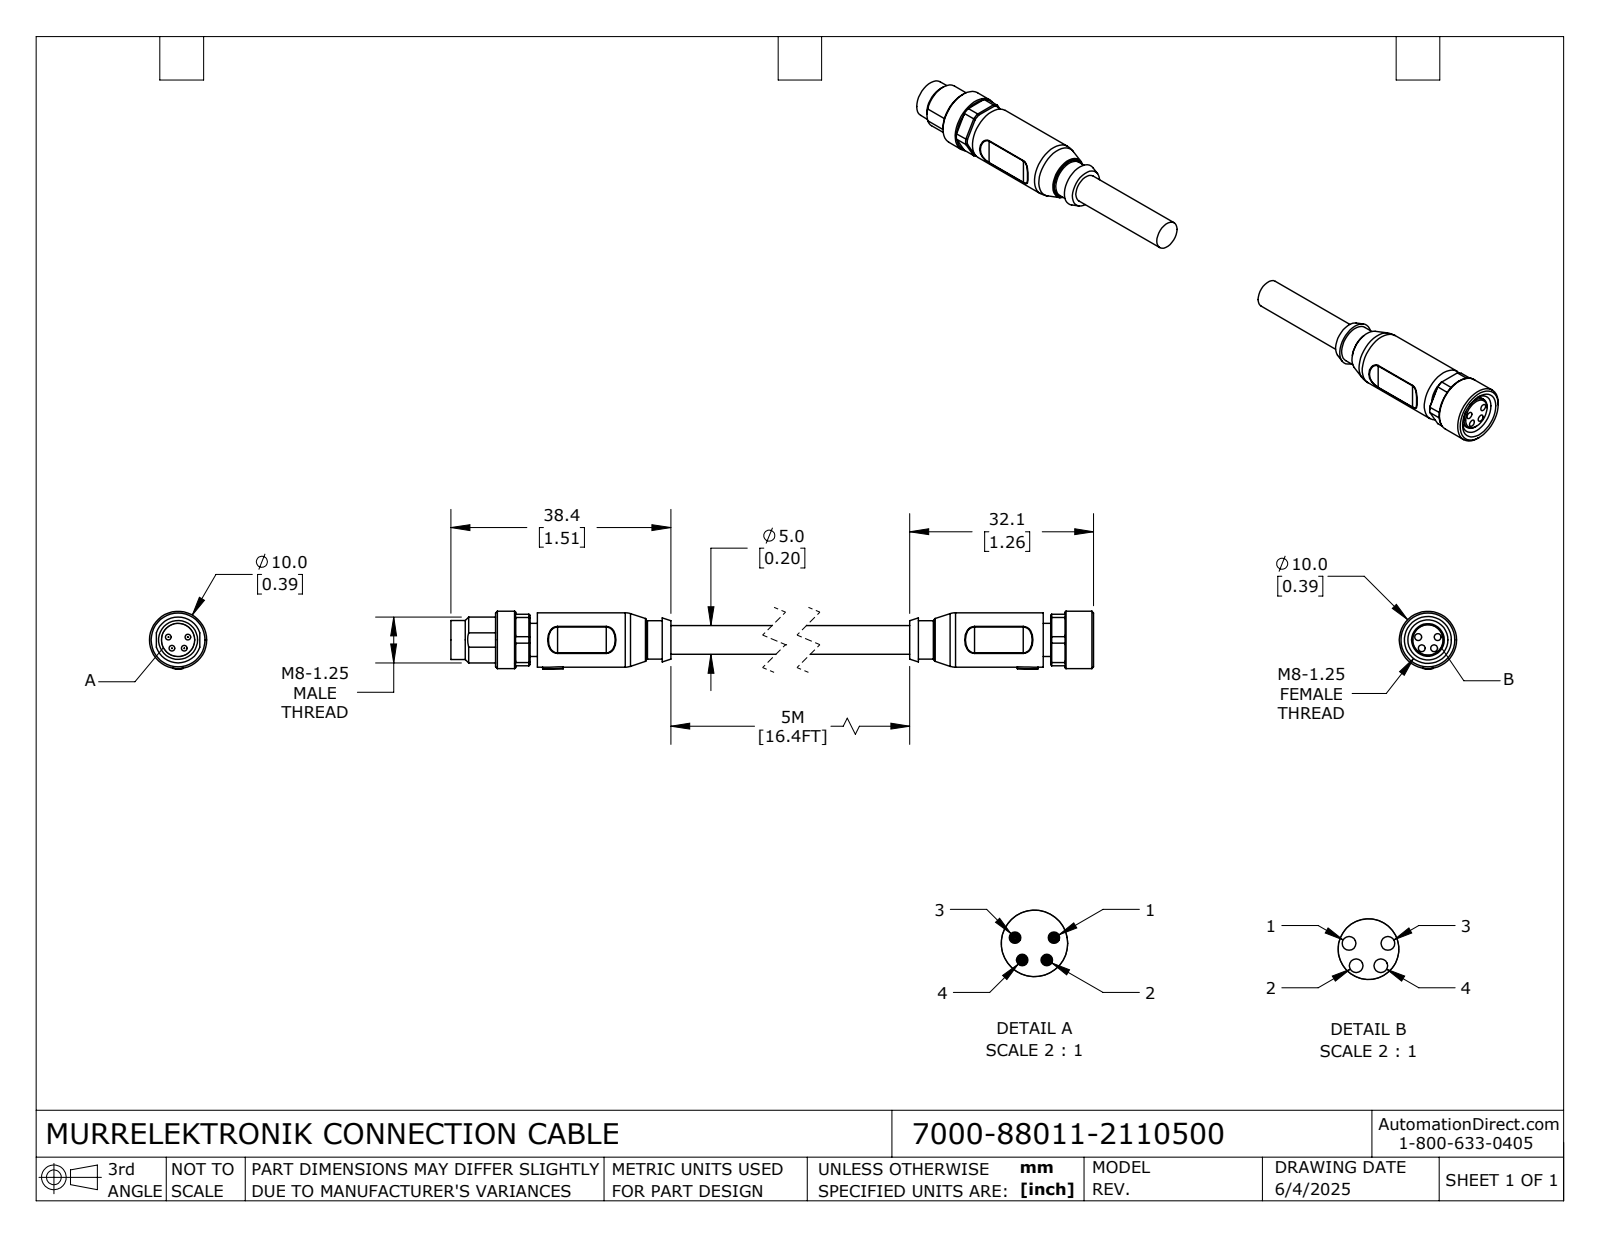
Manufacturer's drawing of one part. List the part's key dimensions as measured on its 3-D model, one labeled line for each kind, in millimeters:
Part name (STEP PRODUCT): 7000-88011-2110500; 7000-88011-2110500_FEMALE; 7000-88011-2110500_MALE
STEP written by: SolidWorks 2024 (CONFIG_CONTROL_DESIGN)
Units: millimetres
Bodies: 2 solids, 226 faces (70 planar, 88 cylindrical, 68 other)
Overall size (bounding box): 135.5 × 10.05 × 10
Volume: 4 815 mm³ · Surface area: 3 452 mm²
Round holes (diameter × count): ⌀1.2 ×4, ⌀7 ×1
Round bosses / shafts (diameter × count): ⌀1 ×4, ⌀10 ×1, ⌀9.5 ×1, ⌀8 ×1, ⌀6.8 ×1, ⌀6.7 ×1, ⌀5.8 ×1, ⌀5.7 ×1
Partial cylindrical surfaces — rounded edges, fillets, slot ends (radius × count): R2.5 ×8, R0.2 ×4, R4.9 ×1, R5.05 ×1
Main face-to-face distances: 8.3, 1.3, 112.9, 9, 121.7, 111.6, 24.6, 8.8, 44.6, 69.6
Hole centre spacings: 1.77, 2.05, 3.4, 1.8, 1.81, 2.15, 3.39
